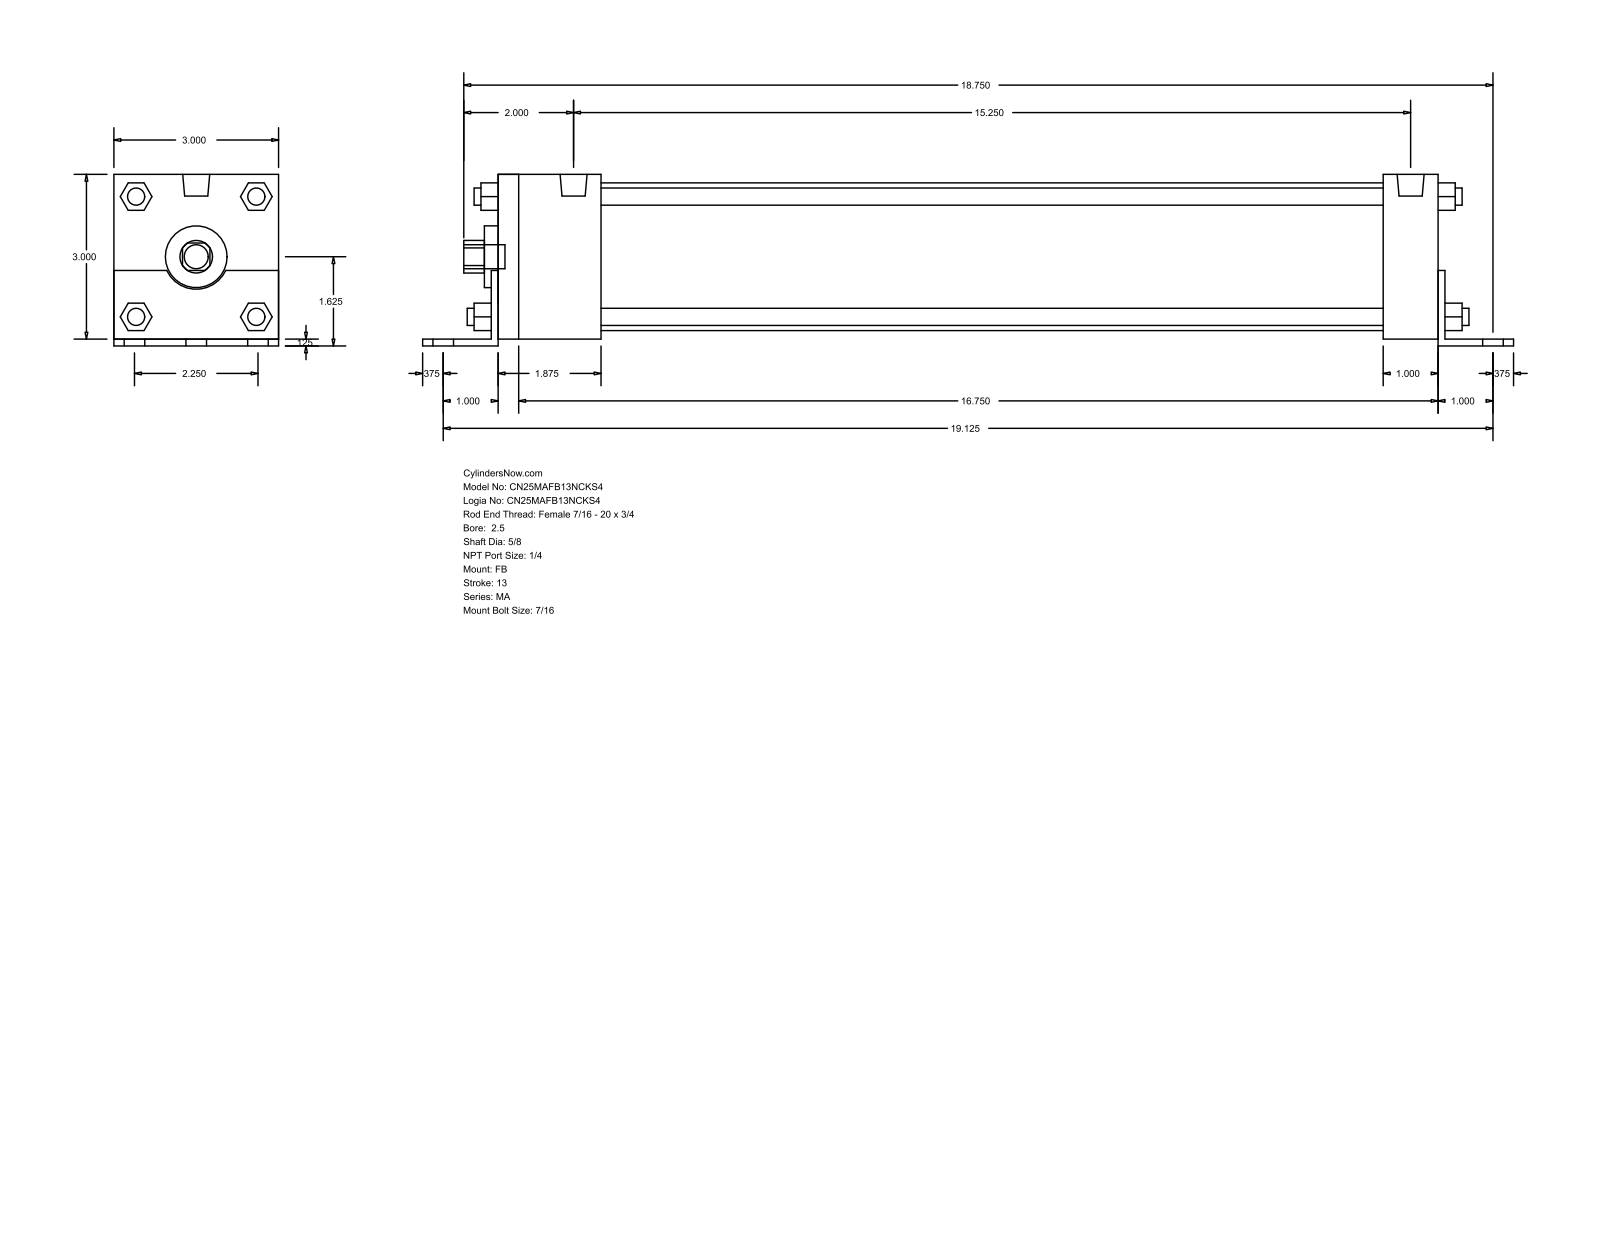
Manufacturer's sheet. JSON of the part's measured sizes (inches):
{"part_name": "MA_FB__0250_0.625", "step_written_by": "GSSL Pune (CONFIG_CONTROL_DESIGN)", "units": "inches", "bodies": {"solids": 0, "faces": 140, "planar": 105, "cylindrical": 35, "other": 0}, "overall_size": [19.875, 3.125, 3], "round_holes": [[0.625, 1], [1.125, 1], [2.69, 1]], "round_bosses_or_shafts": [[0.313, 8], [0.437, 7], [0.492, 2]], "partial_cylinders_radius": [[0.297, 1], [0.593, 1]], "face_to_face_distances": [3, 0.125, 3.125, 17.125, 17.375, 0.125, 17.25, 1.875, 1, 17.25]}
